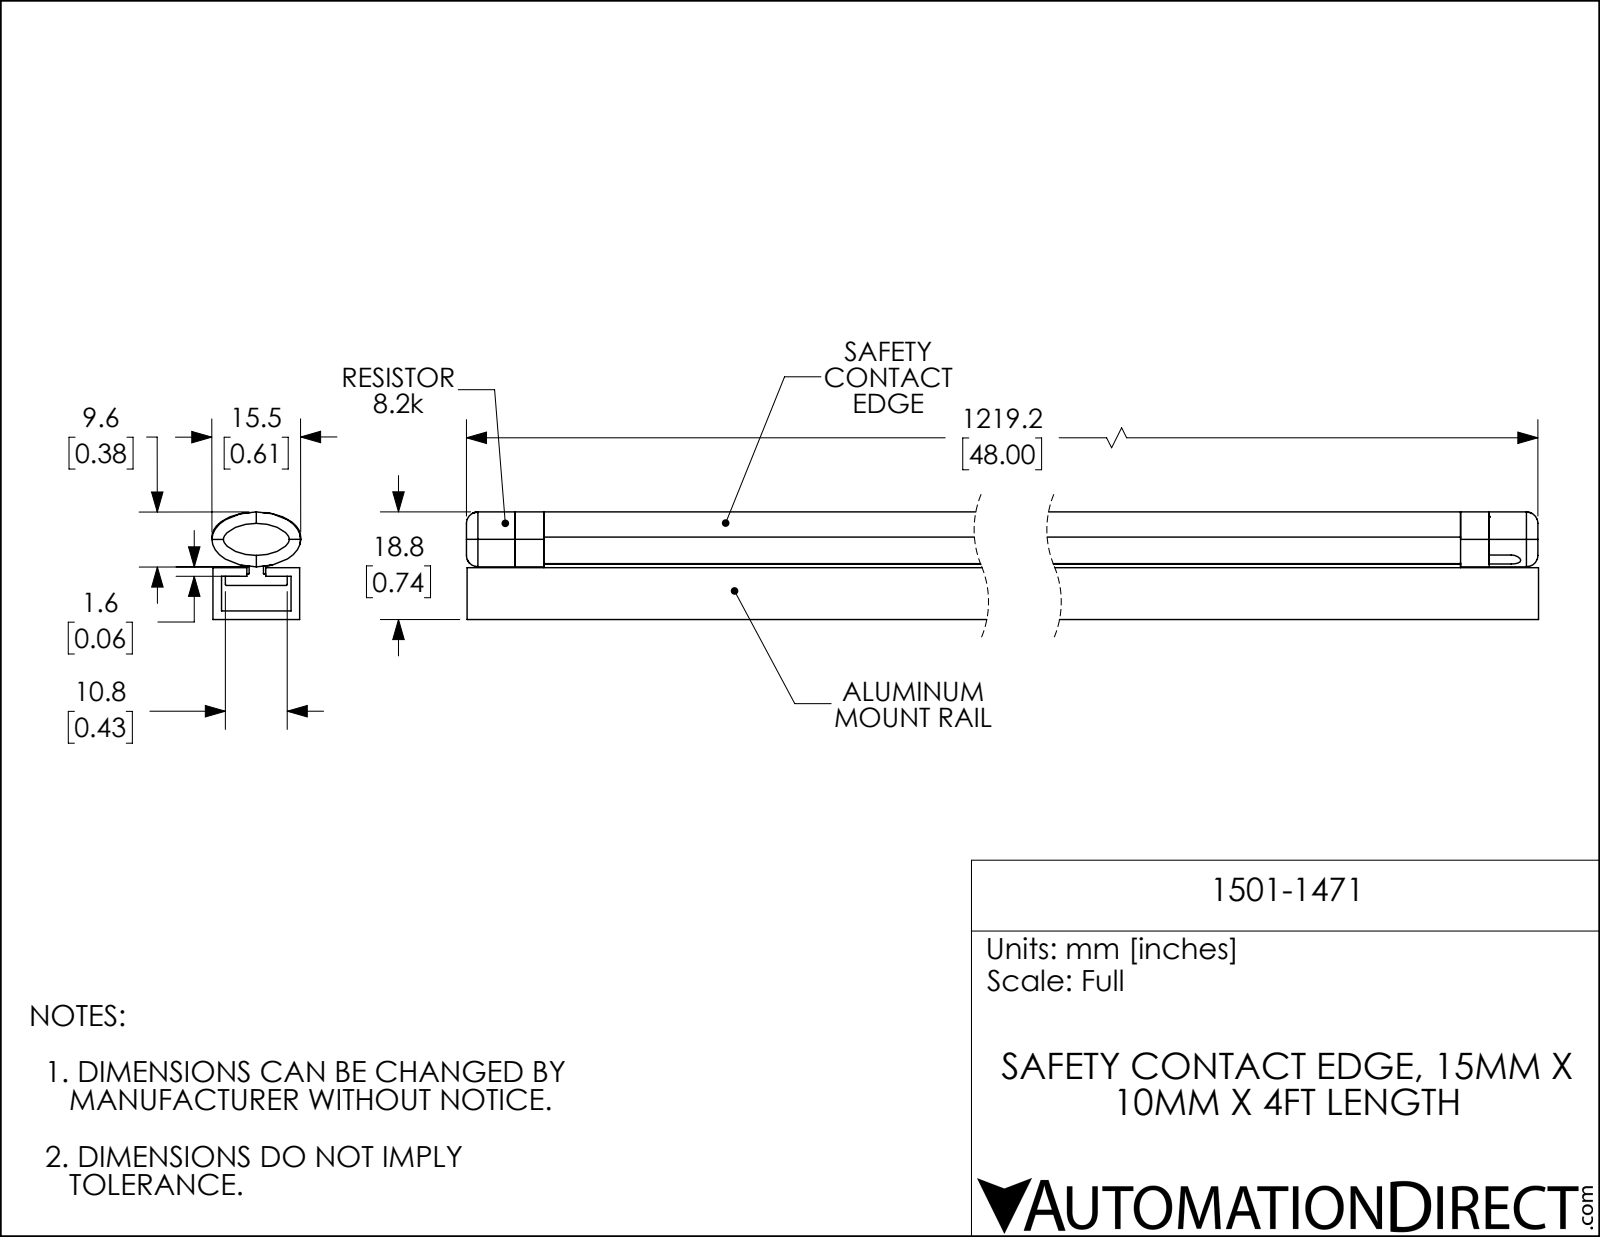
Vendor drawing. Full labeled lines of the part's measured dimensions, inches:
Part name (STEP PRODUCT): 1501-1471
STEP written by: SolidWorks 2018 (AUTOMOTIVE_DESIGN)
Units: inches
Bodies: 7 solids, 607 faces (129 planar, 154 cylindrical, 324 other)
Overall size (bounding box): 49.101 × 2.475 × 0.611
Volume: 11.86 in³ · Surface area: 337 in²
Round holes (diameter × count): ⌀0.047 ×4
Round bosses / shafts (diameter × count): ⌀0.037 ×2
Partial cylindrical surfaces — rounded edges, fillets, slot ends (radius × count): R0.004 ×52, R0.016 ×15, R0.012 ×10, R0.008 ×7, R0.02 ×4, R0.512 ×4, R0.008 ×3, R0.059 ×3
Main face-to-face distances: 0.059, 0.297, 0.537, 0.356, 0.016, 0.122, 0.234, 0.175, 0.596, 0.238
Hole centre spacings: 0.197, 0.196, 0.197
